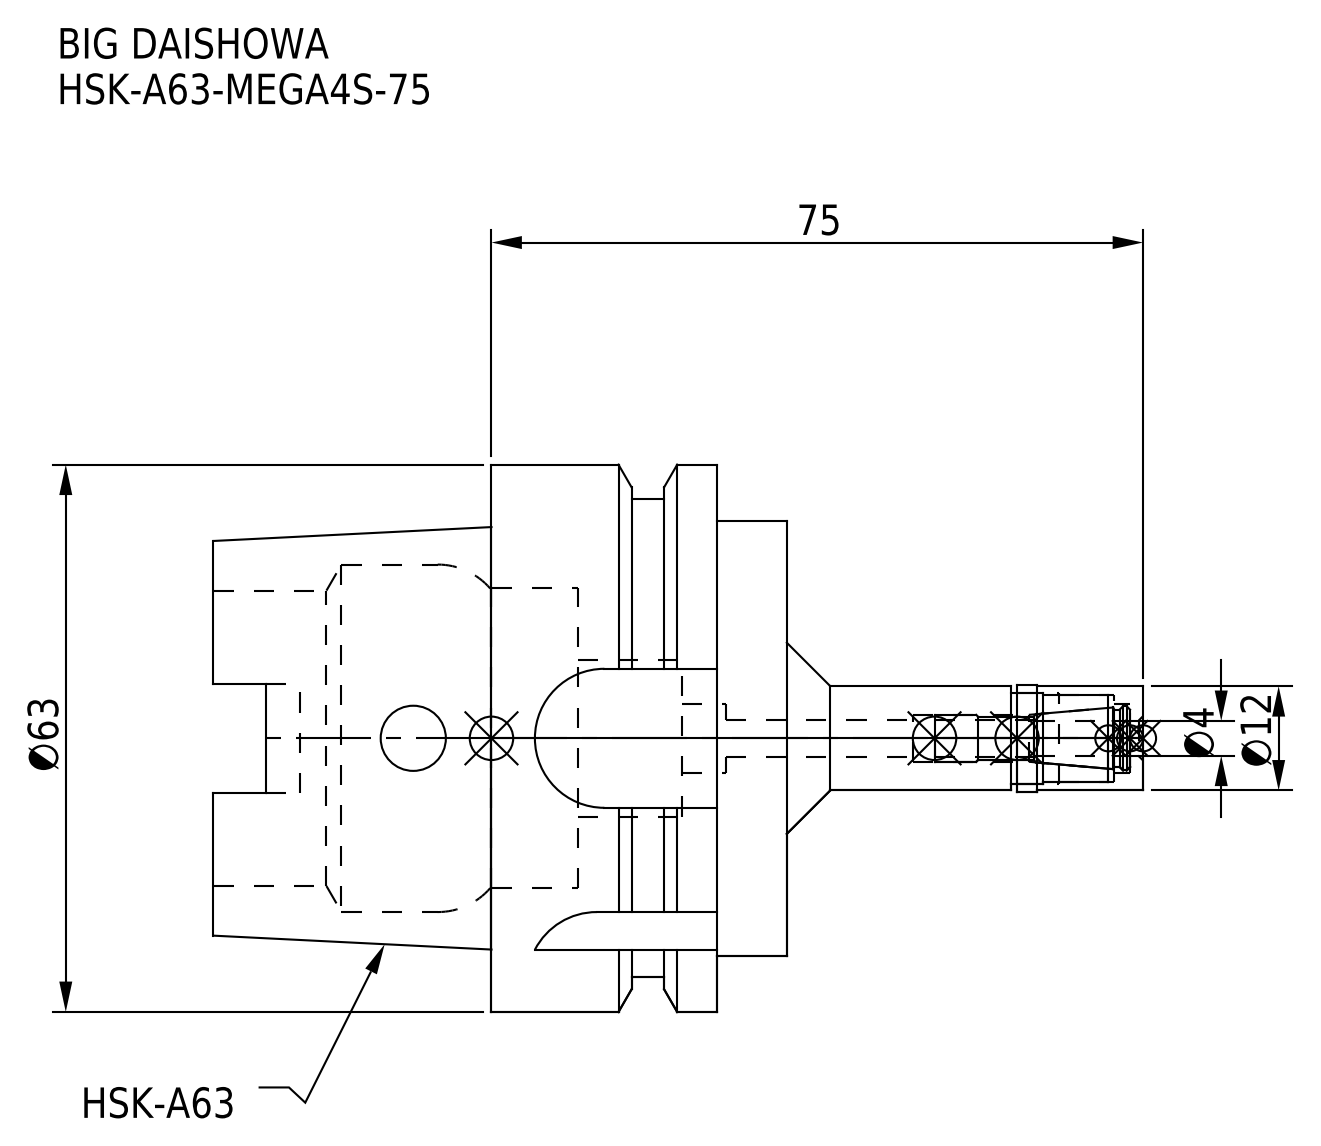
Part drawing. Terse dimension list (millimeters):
name: HSK-A63-MEGA4S-75_1.stp; DXF_TEMP_ASSY_ASM_4_ASM.stp; HSK-A63-MEGA4S-75-040-FreeParts; HSK-A63-MEGA4S-75-040.stp (+3 more)
written by: SolidWorks 2019 (CONFIG_CONTROL_DESIGN)
unit: mm
bodies: 2 solids, 122 faces (47 planar, 55 cylindrical, 20 other)
size: 107 × 63 × 63
volume: 101 448 mm³; area: 26 763 mm²
holes: 1× ⌀4.1, 1× ⌀4.2, 1× ⌀5.4, 1× ⌀7.5, 1× ⌀8, 1× ⌀10, 1× ⌀10.5, 1× ⌀18, 1× ⌀34, 1× ⌀34.5, 1× ⌀40
bosses: 1× ⌀63, 1× ⌀55, 1× ⌀50, 1× ⌀12.3, 1× ⌀12
rounds: 4× R2.88, 4× R8
face distances: 34, 26, 8, 24.05, 16.05, 9.95, 66, 58, 41.95, 32
